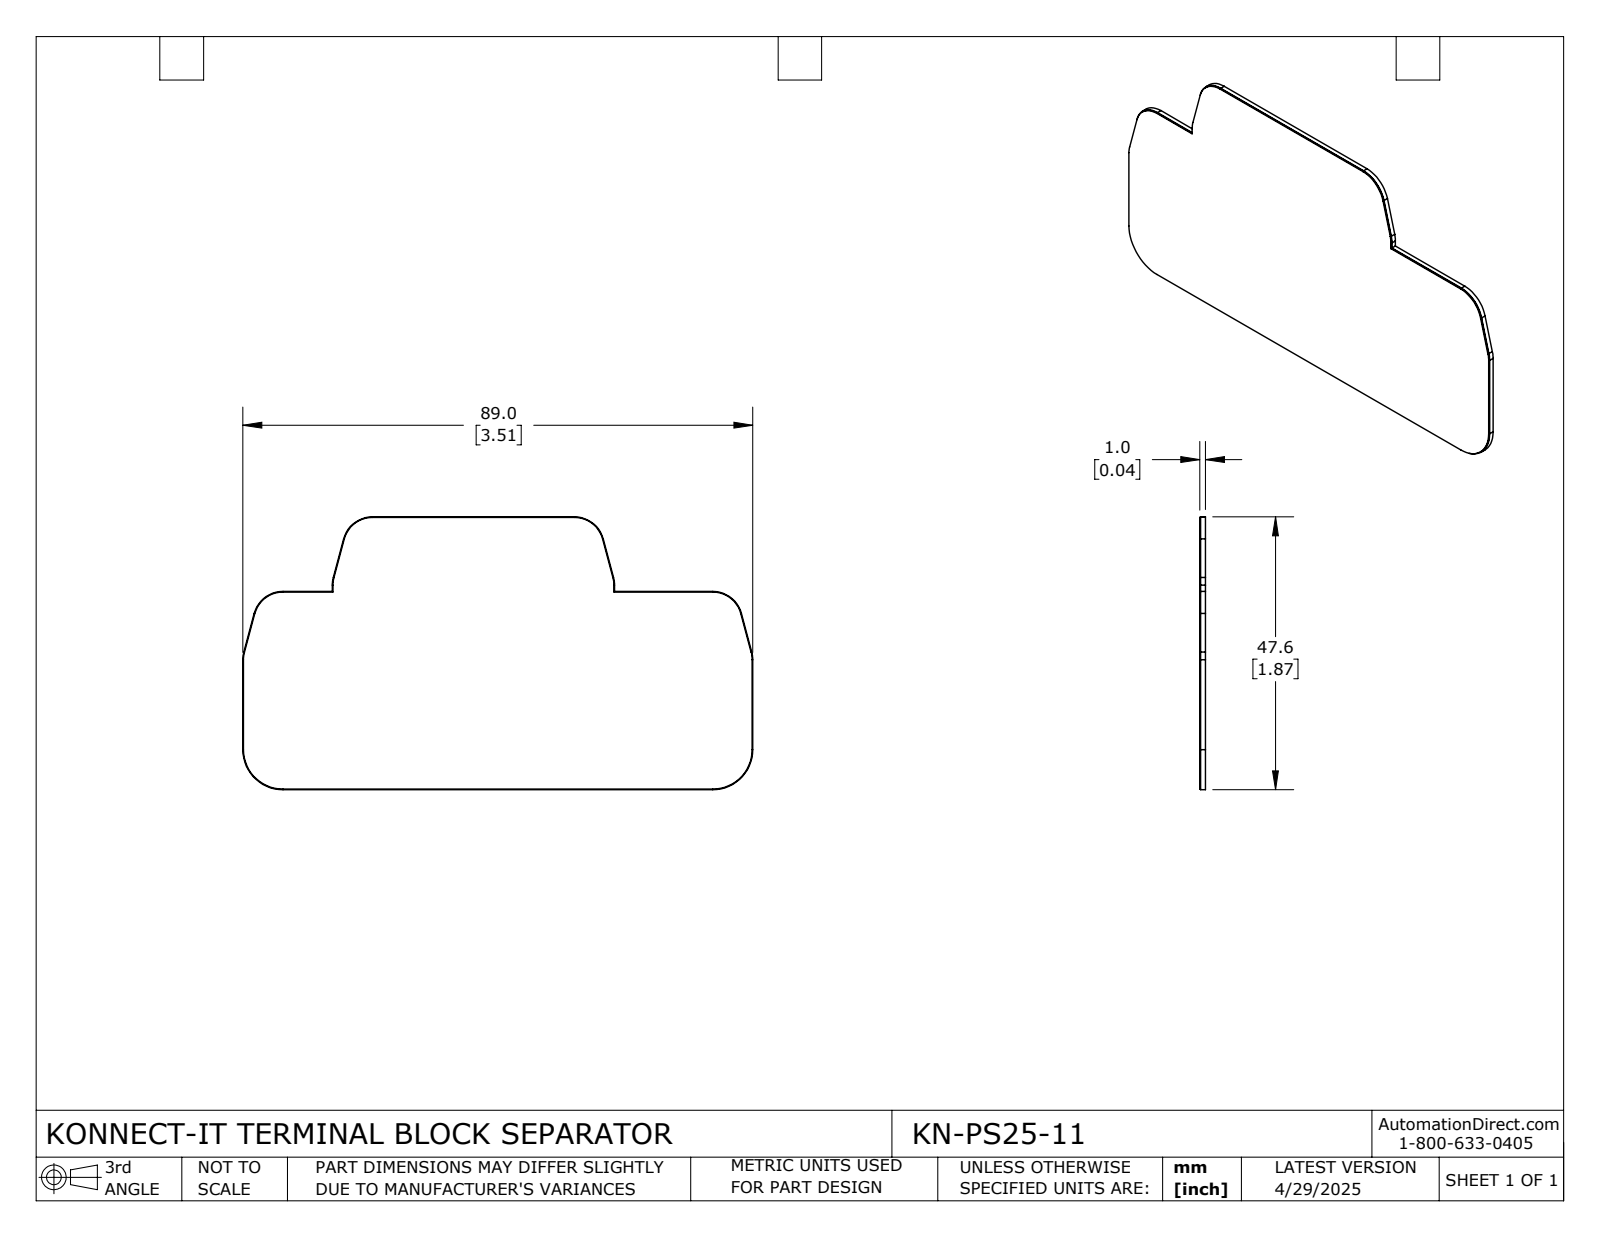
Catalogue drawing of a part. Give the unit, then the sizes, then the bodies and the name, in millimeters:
Units: millimetres
Overall size (bounding box): 89.04 × 47.62 × 1
Partial cylindrical surfaces — rounded edges, fillets, slot ends (radius × count): R5.1 ×8, R5.2 ×8, R6.9 ×2, R7 ×2
Main face-to-face distances: 1, 47.62, 13.01, 0.85, 34.61, 47.52, 34.51, 89.04, 19.94, 11.71
Volume: 3 618 mm³ · Surface area: 7 496 mm²
Bodies: 1 solid, 49 faces (27 planar, 22 cylindrical, 0 other)
Part name (STEP PRODUCT): KN-PS25-11
STEP written by: SolidWorks 2024 (CONFIG_CONTROL_DESIGN)
